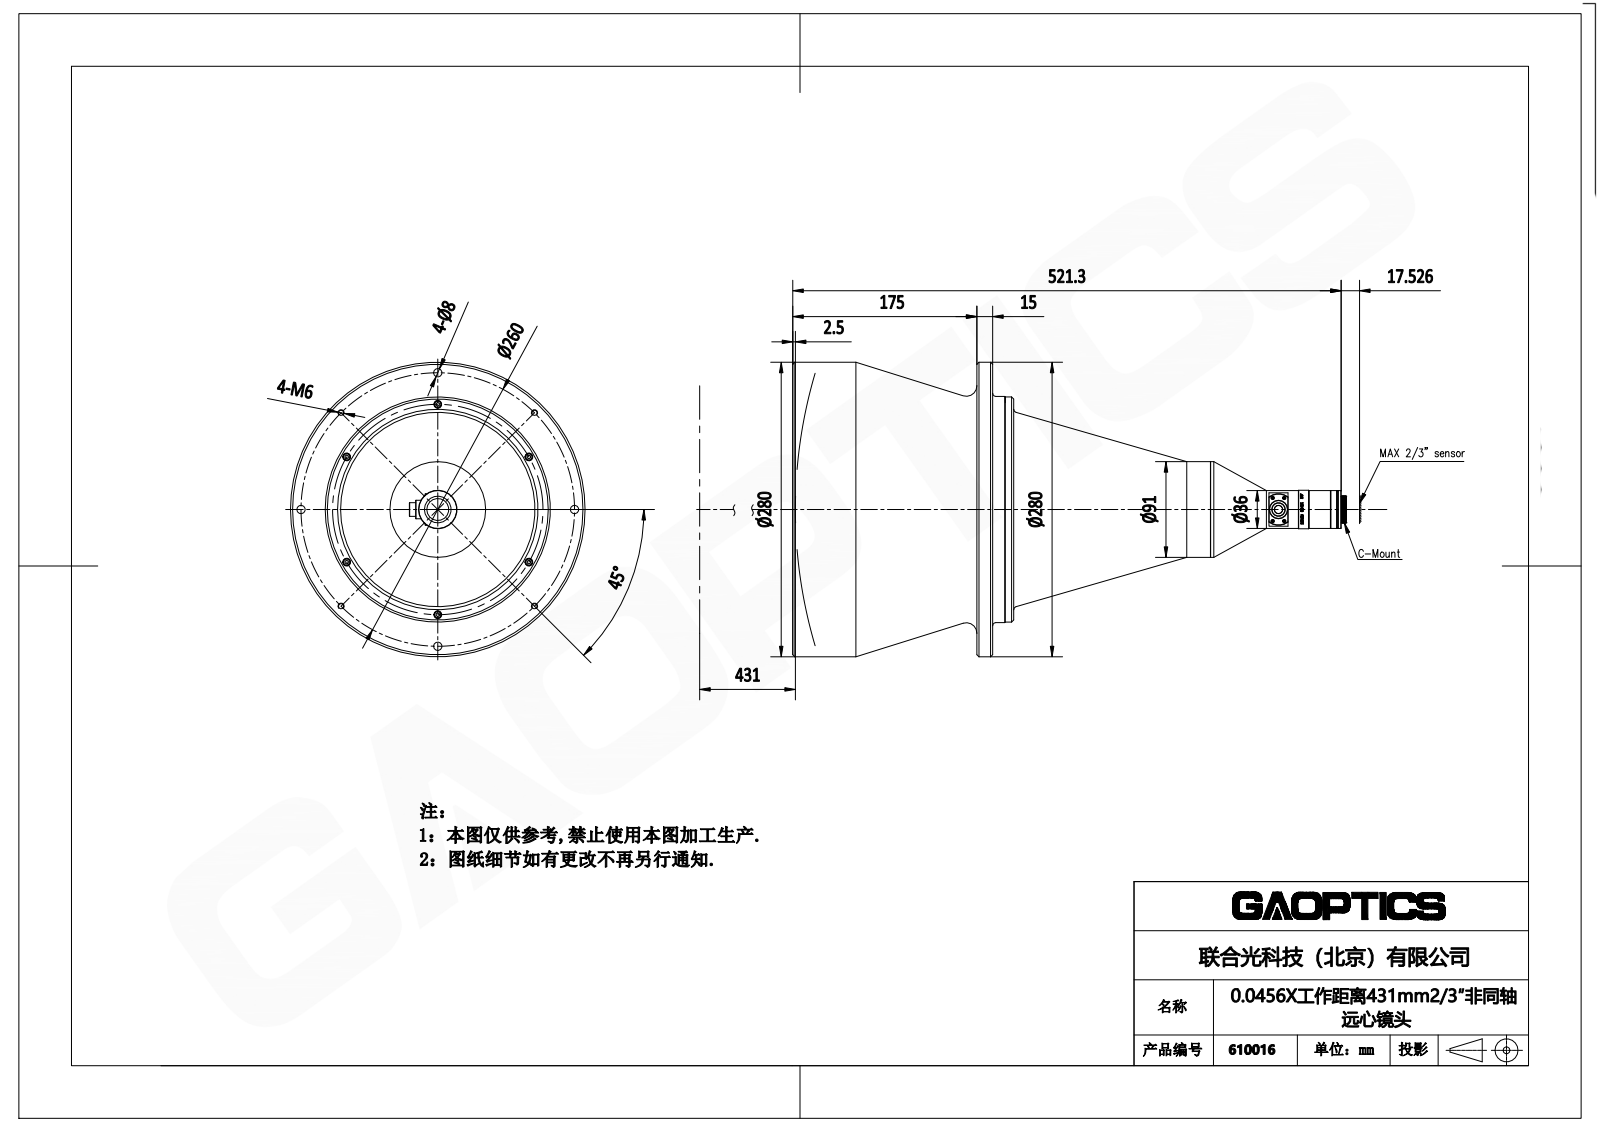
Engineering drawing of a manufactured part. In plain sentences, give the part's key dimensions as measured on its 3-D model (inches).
The part is named "610016". Its 3-D file was written by "SolidWorks 2020 (CONFIG_CONTROL_DESIGN)". It is 0 solids with 807 faces: 283 planar, 118 cylindrical and 406 other. Overall it measures 20.734 by 11.024 by 11.024 inches. Round holes: 6 of diameter 0.276, 1 of diameter 1, 1 of diameter 1.244, 1 of diameter 1.394, 1 of diameter 1.417, 1 of diameter 1.441, 1 of diameter 3.583, 1 of diameter 8.425, 1 of diameter 8.465, 1 of diameter 11.024. Round bosses or shafts: 6 of diameter 0.295, 4 of diameter 0.315, 4 of diameter 0.197, 1 of diameter 10.465, 1 of diameter 10.087, 1 of diameter 0.803. Partial cylindrical surfaces (rounded edges, fillets, slot ends): 1 of radius 0.713, 1 of radius 0.717. The main face-to-face distances are 5.132, 0.591, 4.542, 13.28, 8.738, 8.147, 5.92, 1.378, 0.787, 7.36. The hole center spacings are 3.937, 6.819, 7.874.
